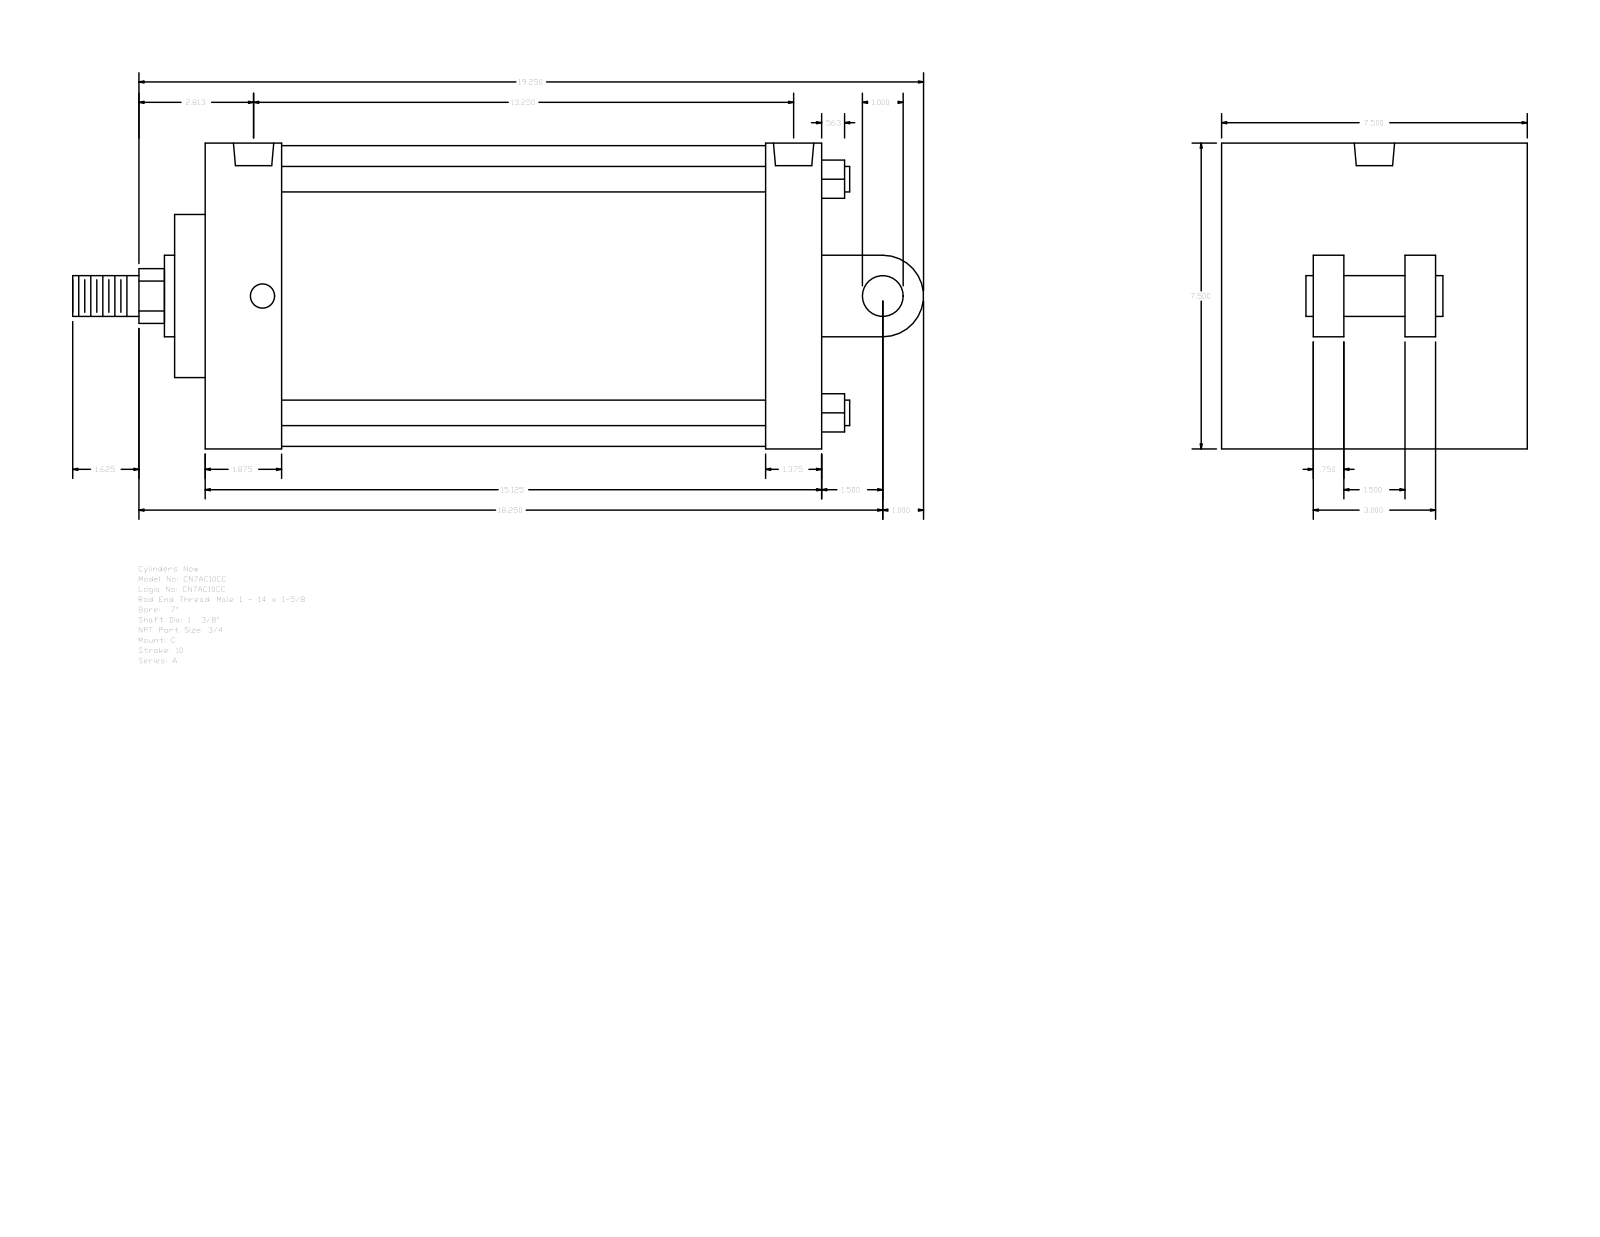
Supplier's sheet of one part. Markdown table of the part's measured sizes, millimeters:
| quantity | value |
| --- | --- |
| part name | A_C__0700_1.375 |
| STEP written by | GSSL Pune (CONFIG_CONTROL_DESIGN) |
| units | millimeters |
| bodies | 0 solids, 104 faces (75 planar, 29 cylindrical, 0 other) |
| overall size | 530.23 × 190.5 × 190.5 |
| round holes (diameter × count) | 15.08 × 4, 25.12 × 2 |
| round bosses / shafts (diameter × count) | 15.88 × 4, 25.4 × 2, 187.32 × 1, 50.8 × 1, 34.92 × 1 |
| partial cylindrical surfaces (radius × count) | 17.06 × 1, 25.4 × 1 |
| main face-to-face distances | 190.5, 384.18, 76.2, 57.15, 19.04, 403.22, 66.67, 47.63, 336.55, 368.29 |
| hole center spacings | 5.56, 325.43, 330.99, 336.55 |
